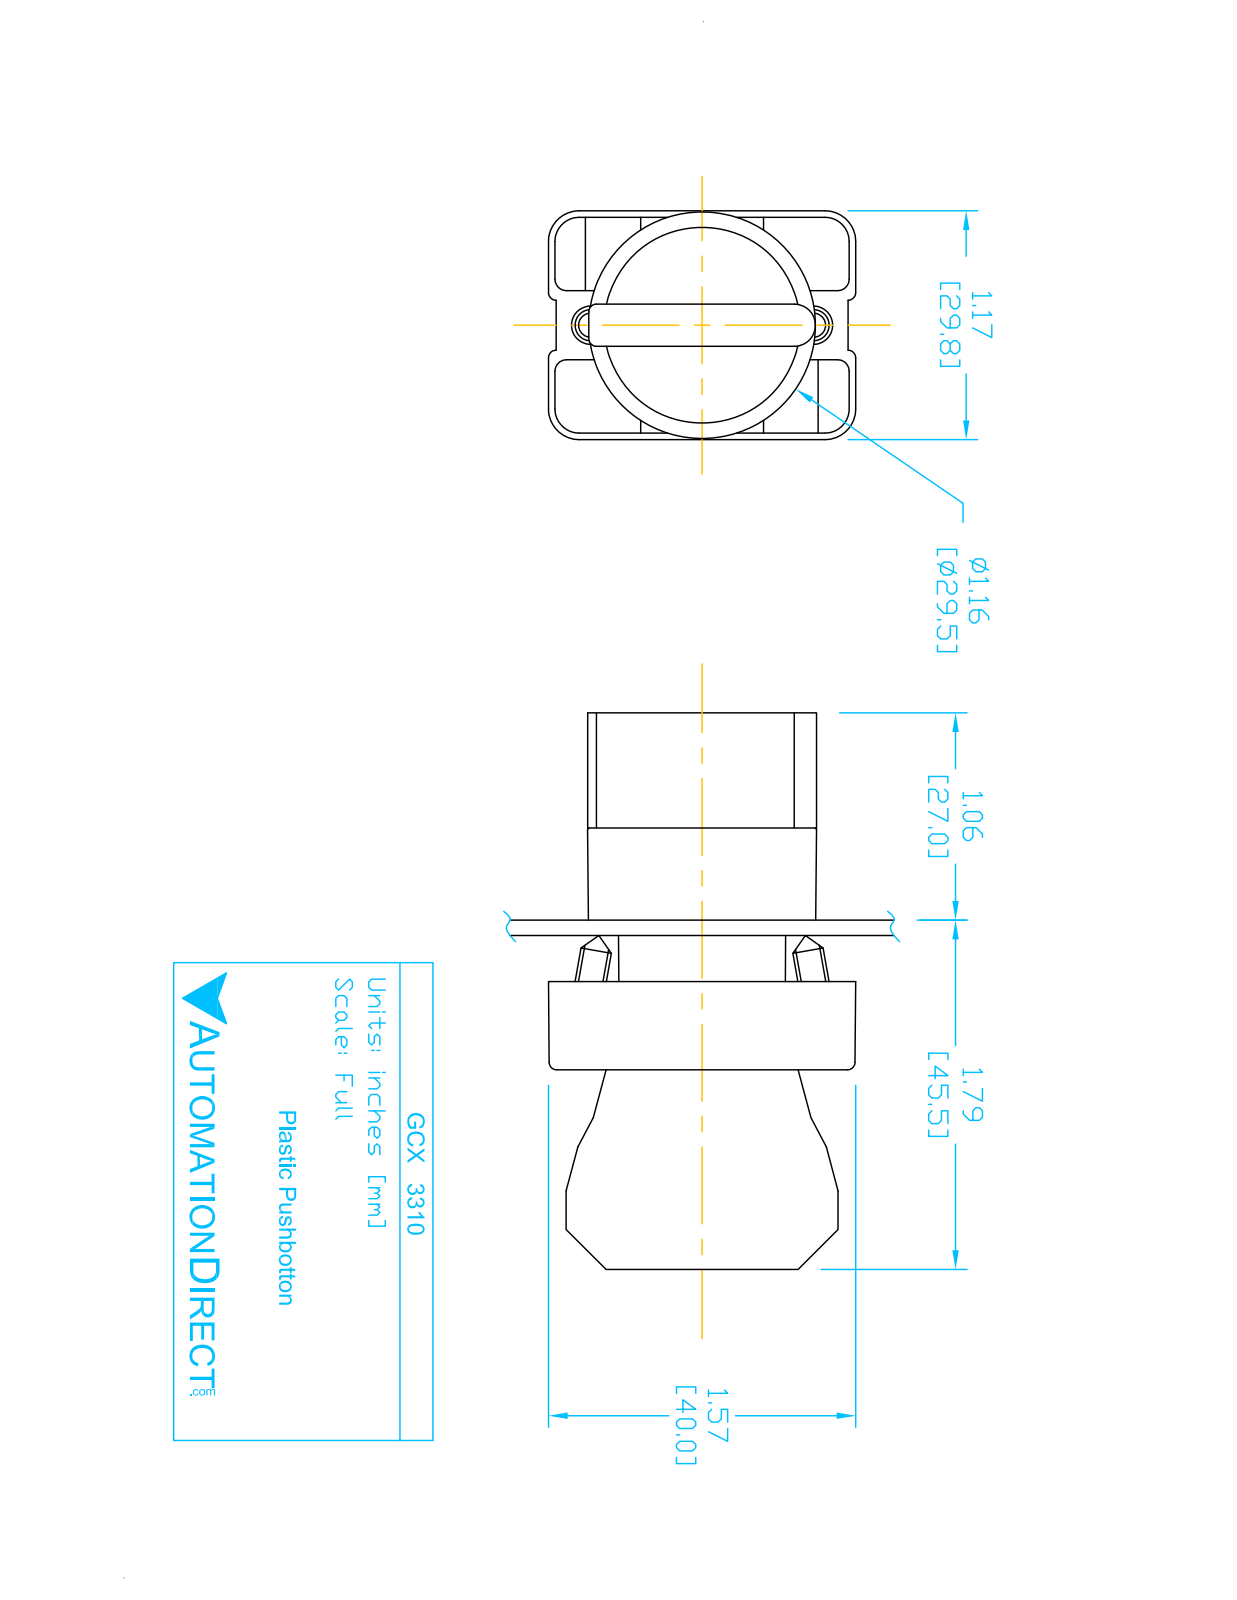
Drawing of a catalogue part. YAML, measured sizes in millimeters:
part_name: "ecx1040; GCX3310; ECX3029-2; GCX3310 OPERATOR"
step_written_by: "SolidWorks 2016 (AUTOMOTIVE_DESIGN)"
units: millimeters
bodies: {solids: 6, faces: 396, planar: 232, cylindrical: 137, other: 27}
overall_size: [70.6, 40.2, 29.9]
volume: 30810
surface_area: 18480
round_holes:
  - {diameter: 2, count: 2}
  - {diameter: 3.1, count: 2}
  - {diameter: 3.3, count: 2}
  - {diameter: 2.2, count: 1}
  - {diameter: 5, count: 1}
  - {diameter: 22.3, count: 1}
  - {diameter: 22.6, count: 1}
  - {diameter: 26, count: 1}
round_bosses_or_shafts:
  - {diameter: 4, count: 2}
  - {diameter: 29.8, count: 1}
  - {diameter: 25.5, count: 1}
  - {diameter: 24, count: 1}
  - {diameter: 21.7, count: 1}
  - {diameter: 19.8, count: 1}
partial_cylinders:
  - {radius: 1.5, count: 24}
  - {radius: 1, count: 12}
  - {radius: 3.1, count: 12}
  - {radius: 4, count: 12}
  - {radius: 1, count: 6}
  - {radius: 3.3, count: 2}
  - {radius: 0.5, count: 1}
  - {radius: 1.6, count: 1}
face_to_face_distances: [18.3, 14.7, 0.8, 12, 0.8, 12, 17.9, 17.5, 30.3, 15.2]
hole_center_spacings: [6, 13.8, 12, 12.4]
